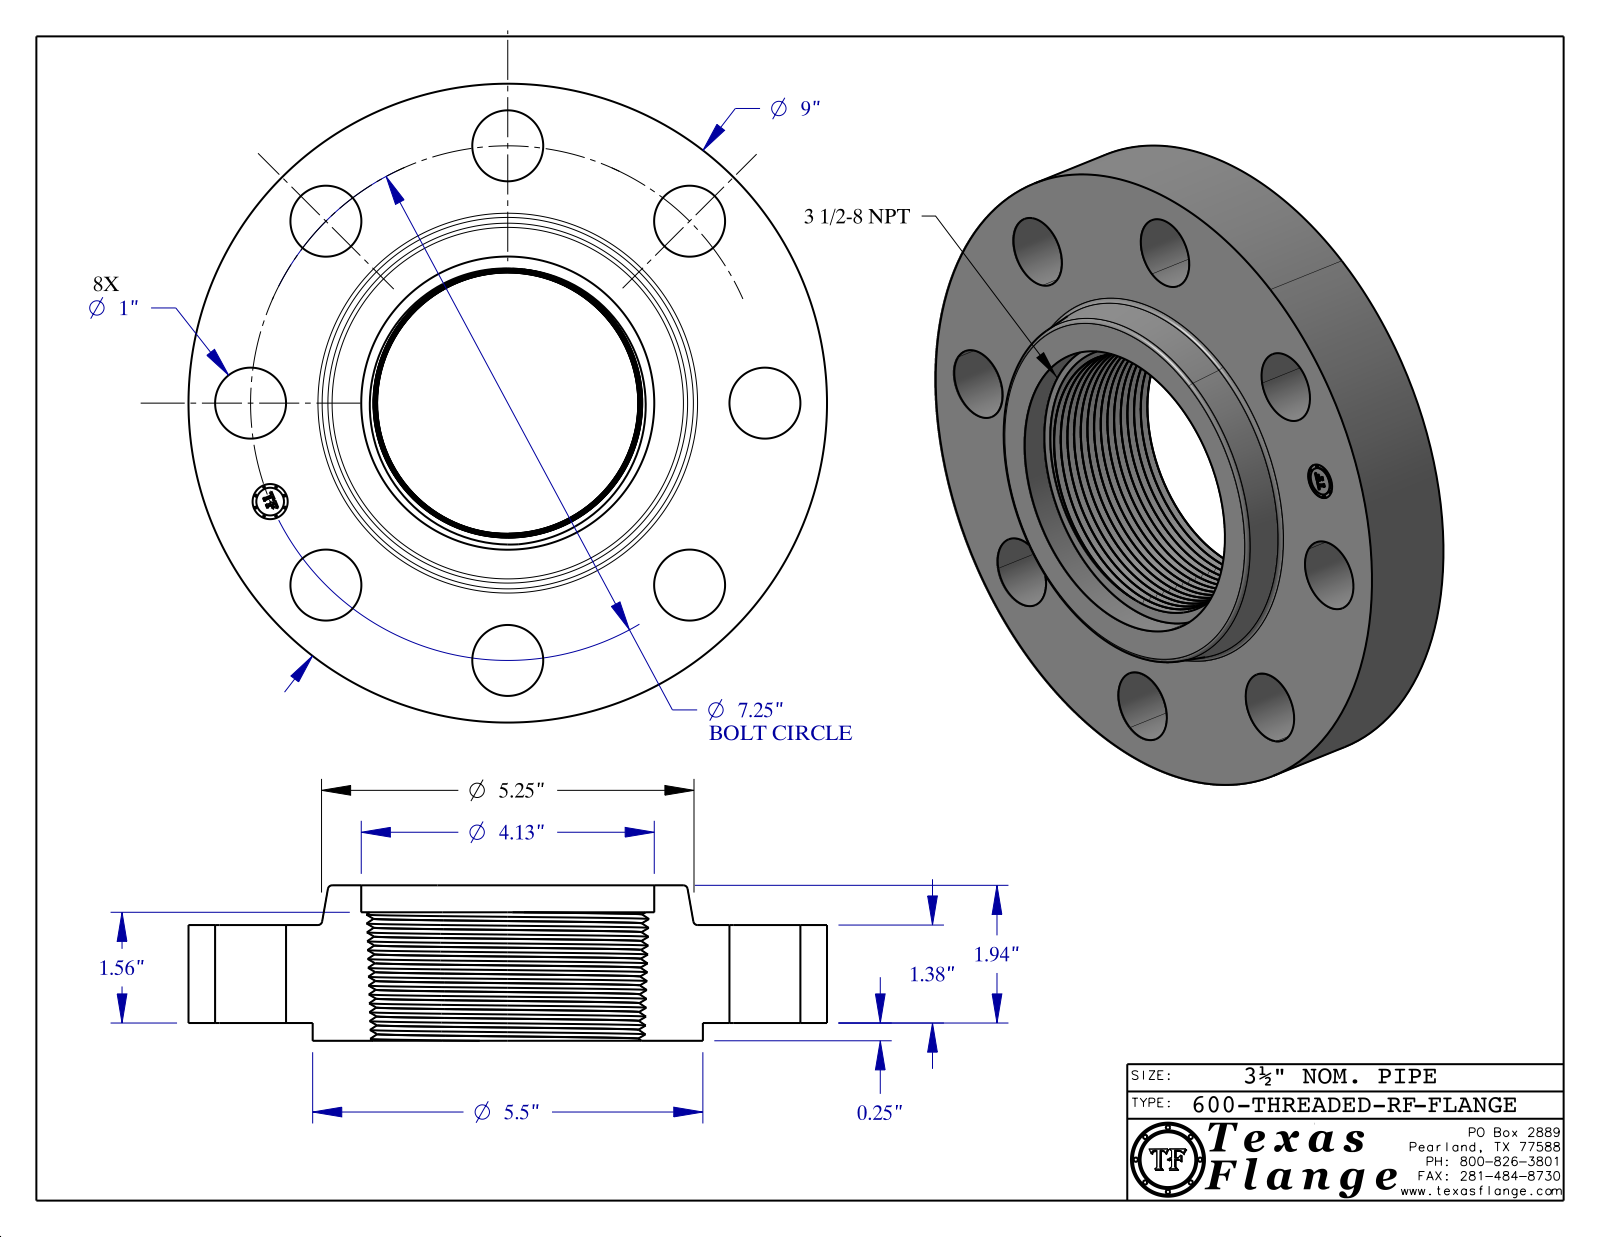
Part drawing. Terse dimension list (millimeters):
name: 600-THREADED-RF
written by: CATIA V5 STEP AP214 (AUTOMOTIVE_DESIGN)
unit: mm
bodies: 1 solid, 569 faces (370 planar, 42 cylindrical, 157 other)
size: 228.6 × 228.6 × 55.6
volume: 1 160 000 mm³; area: 143 600 mm²
holes: 8× ⌀25.4, 1× ⌀12.6, 1× ⌀104.9
bosses: 8× ⌀0.8, 1× ⌀228.6, 1× ⌀139.7, 1× ⌀9.9
face distances: 35.1, 6.4, 41.4, 55.6, 49.3, 14.2, 46, 39.6, 4.6, 9.7
hole spacings: 92.1, 70.5, 130.2, 170.1, 184.2, 35.9, 180.6, 102.3
